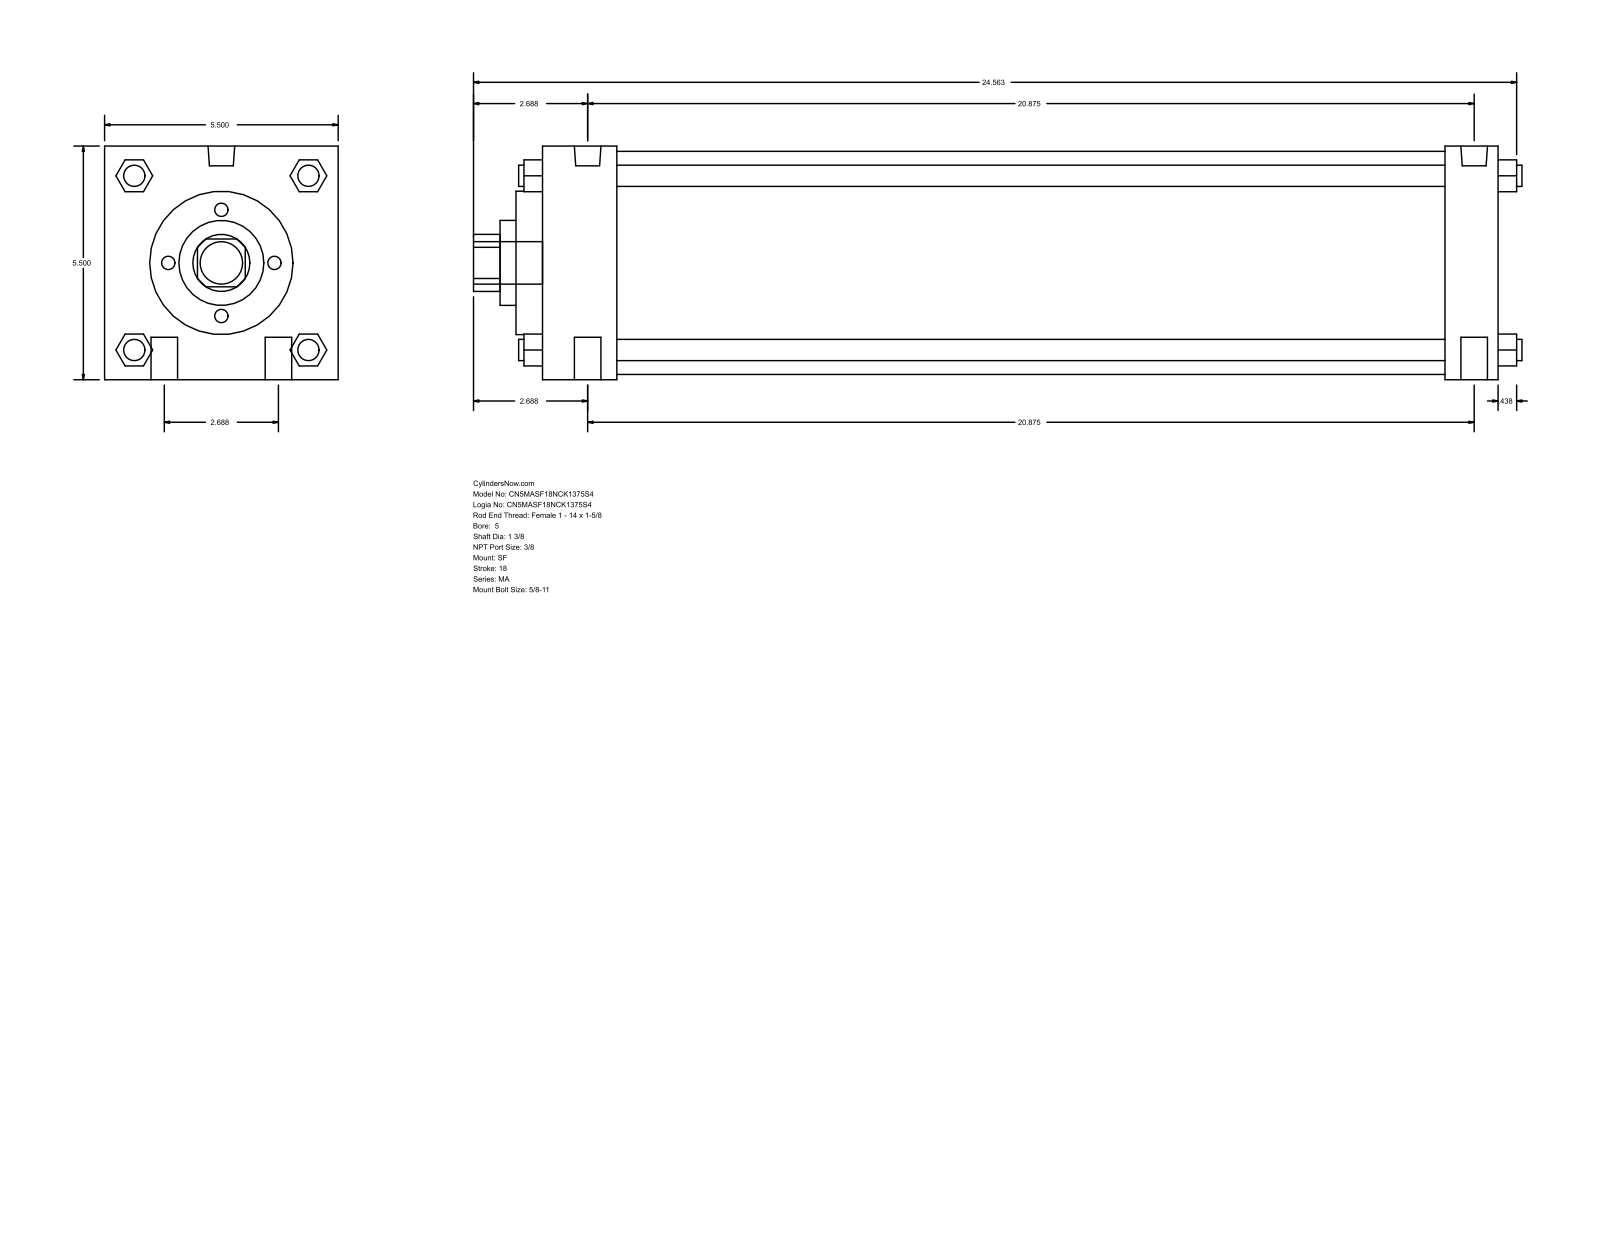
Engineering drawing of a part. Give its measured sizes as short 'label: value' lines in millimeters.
name: MA_SF__0500_1.375
written by: GSSL Pune (CONFIG_CONTROL_DESIGN)
unit: mm
bodies: 0 solids, 126 faces (95 planar, 31 cylindrical, 0 other)
size: 627.06 × 139.7 × 139.7
holes: 1× ⌀34.92, 1× ⌀50.8, 1× ⌀85.72, 1× ⌀133.35
bosses: 4× ⌀15.88, 4× ⌀12.7, 2× ⌀15.93, 2× ⌀11.11, 1× ⌀25.4
rounds: 1× R17.06
face distances: 139.7, 571.5, 44.45, 539.75, 495.3, 527.05, 31.75, 15.87, 60.32, 555.62
